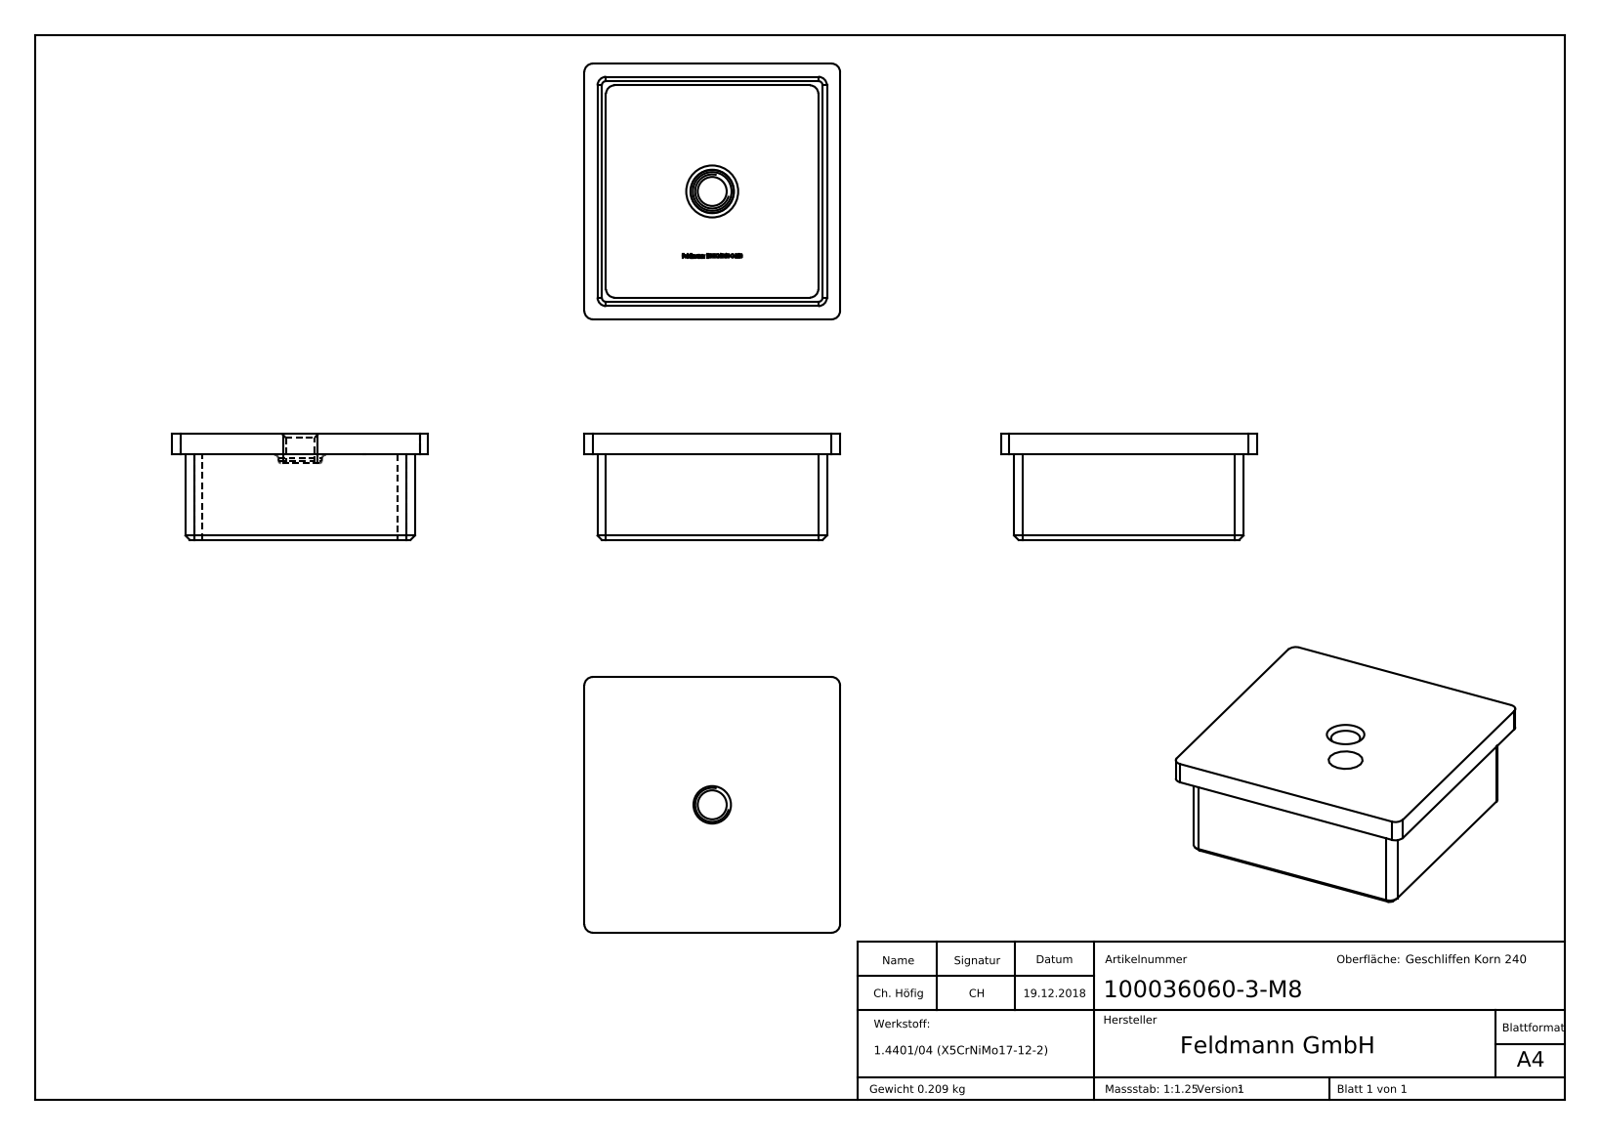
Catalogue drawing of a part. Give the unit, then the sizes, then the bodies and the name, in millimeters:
Units: millimetres
Overall size (bounding box): 60 × 60 × 25
Round holes (diameter × count): ⌀6.8 ×1
Partial cylindrical surfaces — rounded edges, fillets, slot ends (radius × count): R2 ×12
Main face-to-face distances: 2, 51.8, 5, 53.8, 49.8, 3.1, 5.1, 54.9, 56.9, 60
Volume: 26 067 mm³ · Surface area: 16 517 mm²
Bodies: 1 solid, 330 faces (148 planar, 14 cylindrical, 168 other)
Part name (STEP PRODUCT): 100036060-3-M8
STEP written by: SolidWorks 2015 (CONFIG_CONTROL_DESIGN)
